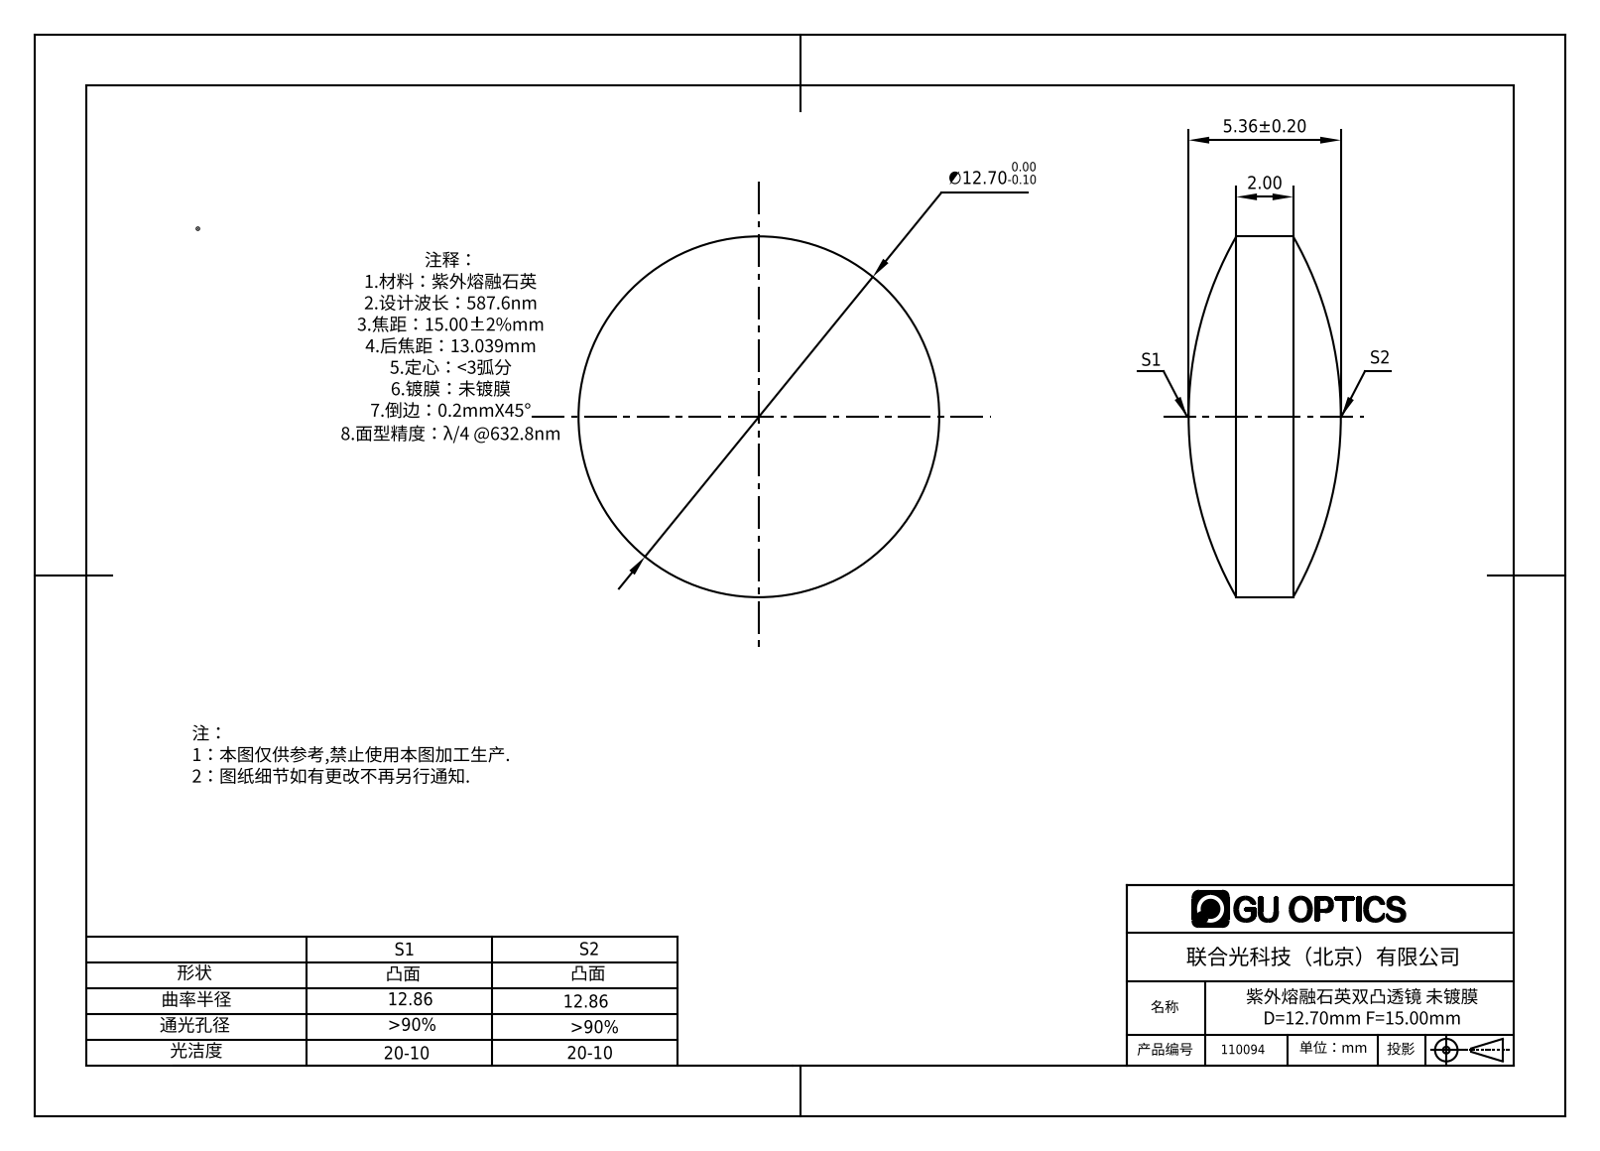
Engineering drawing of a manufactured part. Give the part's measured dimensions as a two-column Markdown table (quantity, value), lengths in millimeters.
| quantity | value |
| --- | --- |
| part name | 110094 |
| STEP written by | SolidWorks 2016 (CONFIG_CONTROL_DESIGN) |
| units | millimeters |
| bodies | 1 solid, 6 faces (0 planar, 2 cylindrical, 4 other) |
| overall size | 12.7 × 12.7 × 5.36 |
| volume | 471 mm³ |
| surface area | 351 mm² |
| round bosses / shafts (diameter × count) | 12.7 × 1 |
